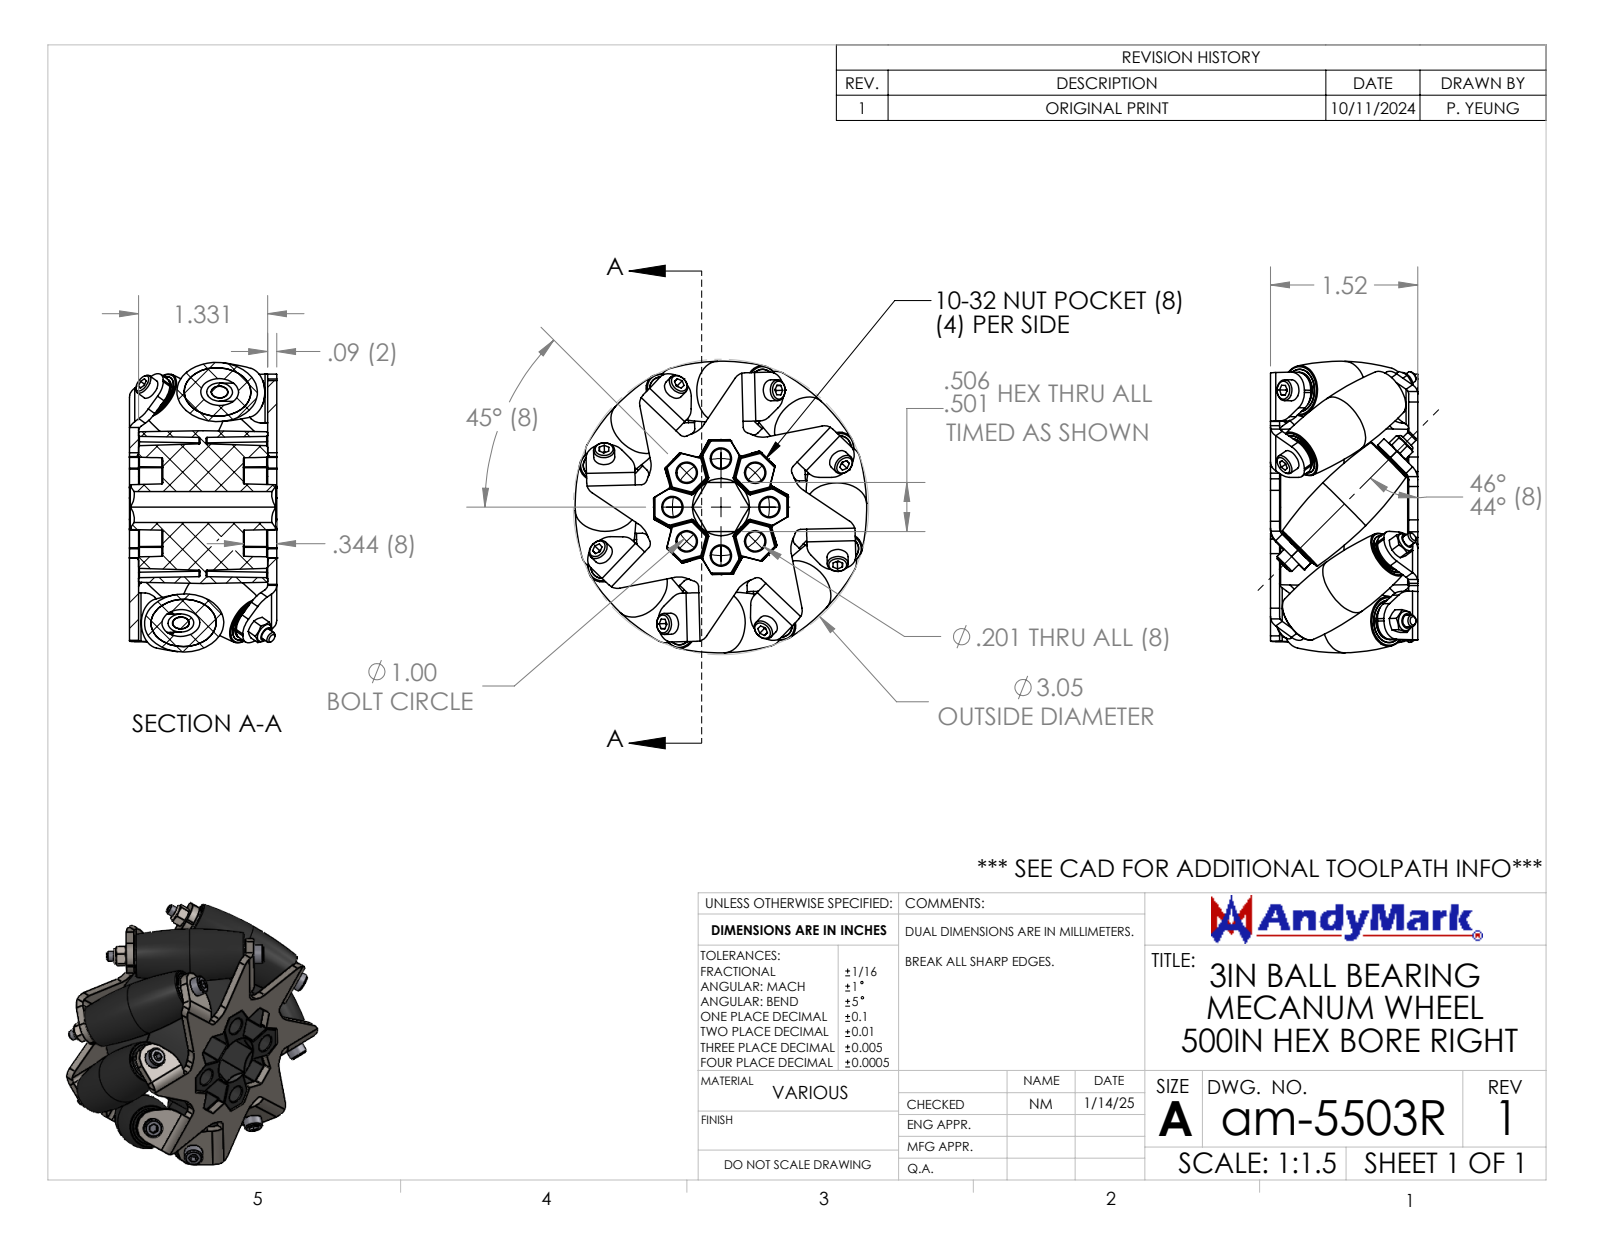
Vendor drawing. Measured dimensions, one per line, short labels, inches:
name: am-4764 4IN BB Mecanum Axle Sleeve; SHCS M3 x 45mm; 4IN BB Mecanum Roller Assy_Extended Inner Race Bearing; 4IN BB Mecanum Roller Core (+6 more)
written by: SolidWorks 2024 (AUTOMOTIVE_DESIGN)
unit: in
bodies: 299 solids, 2961 faces (644 planar, 1026 cylindrical, 1291 other)
size: 3.005 × 3.005 × 1.519
volume: 5.08 in³; area: 142.9 in²
holes: 14× ⌀0.134, 14× ⌀0.187, 14× ⌀0.234, 14× ⌀0.303, 14× ⌀0.438, 8× ⌀0.123, 8× ⌀0.125, 8× ⌀0.201, 8× ⌀0.276, 8× ⌀0.375
bosses: 14× ⌀0.375, 8× ⌀0.217, 8× ⌀0.118
rounds: 264× R0.01, 32× R0.25, 21× R0.188, 16× R0.09, 16× R0.125, 16× R0.184, 10× R0.062, 8× R0.187
face distances: 0.094, 1.425, 1.331, 1.441, 1.519, 0.505, 1.347, 1.179, 1.18, 1.441
hole spacings: 0.383, 0.707, 0.924, 1
